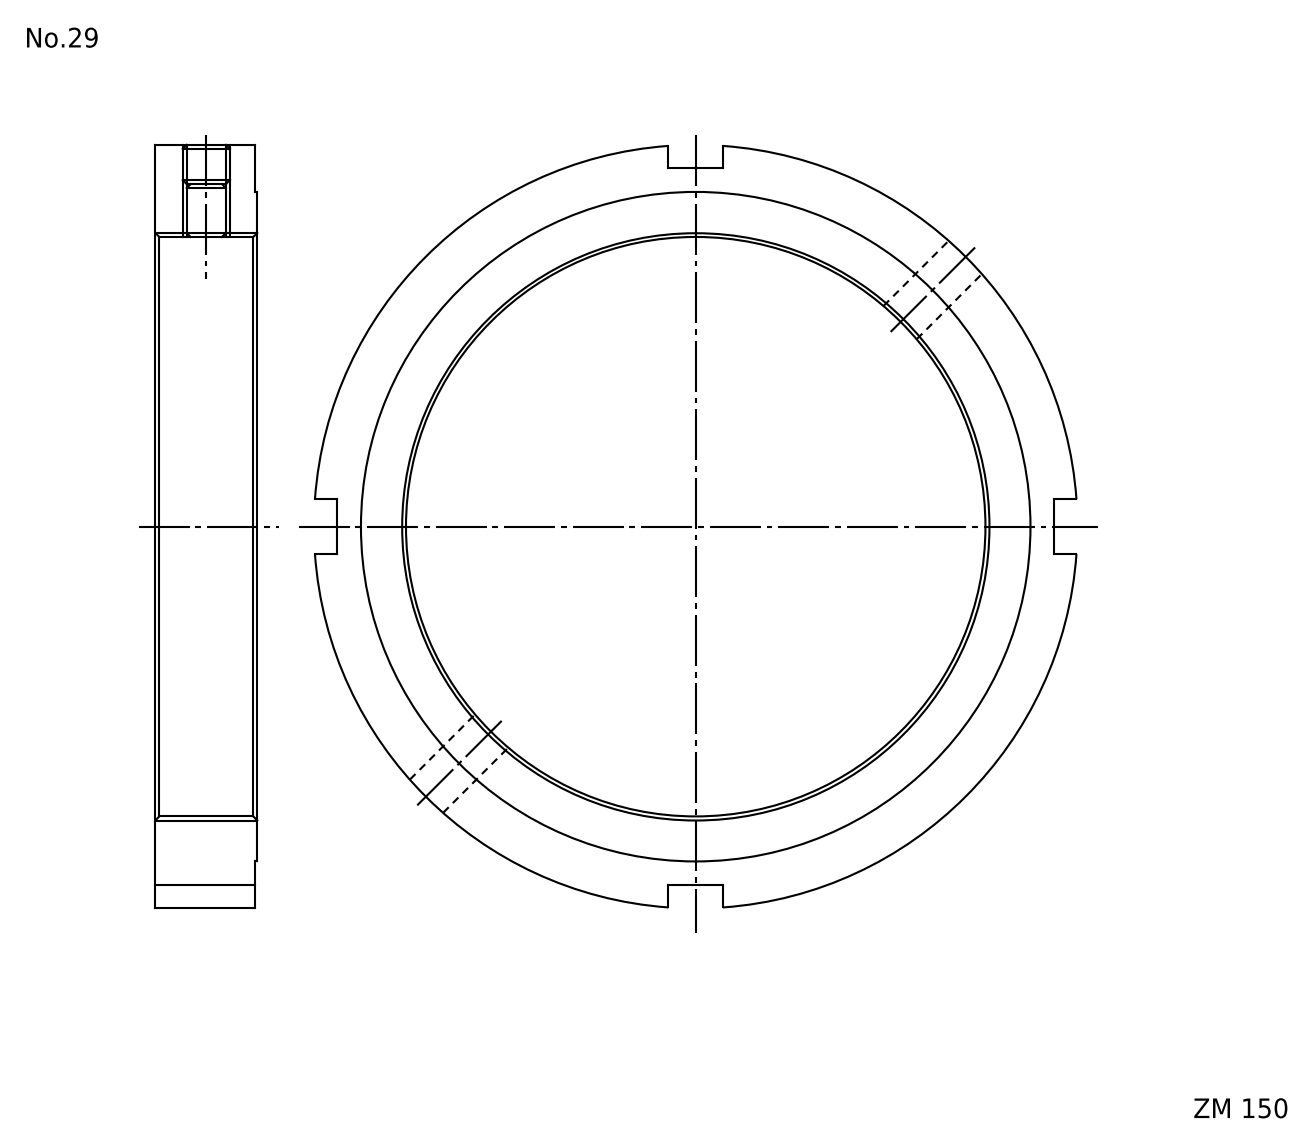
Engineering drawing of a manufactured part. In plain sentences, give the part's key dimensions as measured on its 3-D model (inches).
The part is named "FKD ZM150". Its 3-D file was written by "Autodesk Inventor 2011 (AUTOMOTIVE_DESIGN)". It is 1 solid with 23 faces: 15 planar, 8 cylindrical and 0 other. Overall it measures 7.657 by 7.657 by 1.024 inches. Its volume is 18.4 cubic inches and its surface area 83.93 square inches. Round holes: 2 of diameter 0.398, 1 of diameter 5.906. Round bosses or shafts: 1 of diameter 7.677, 1 of diameter 6.732. The main face-to-face distances are 1.004, 0.02, 1.024, 3.327, 3.878, 7.205, 0.551.
